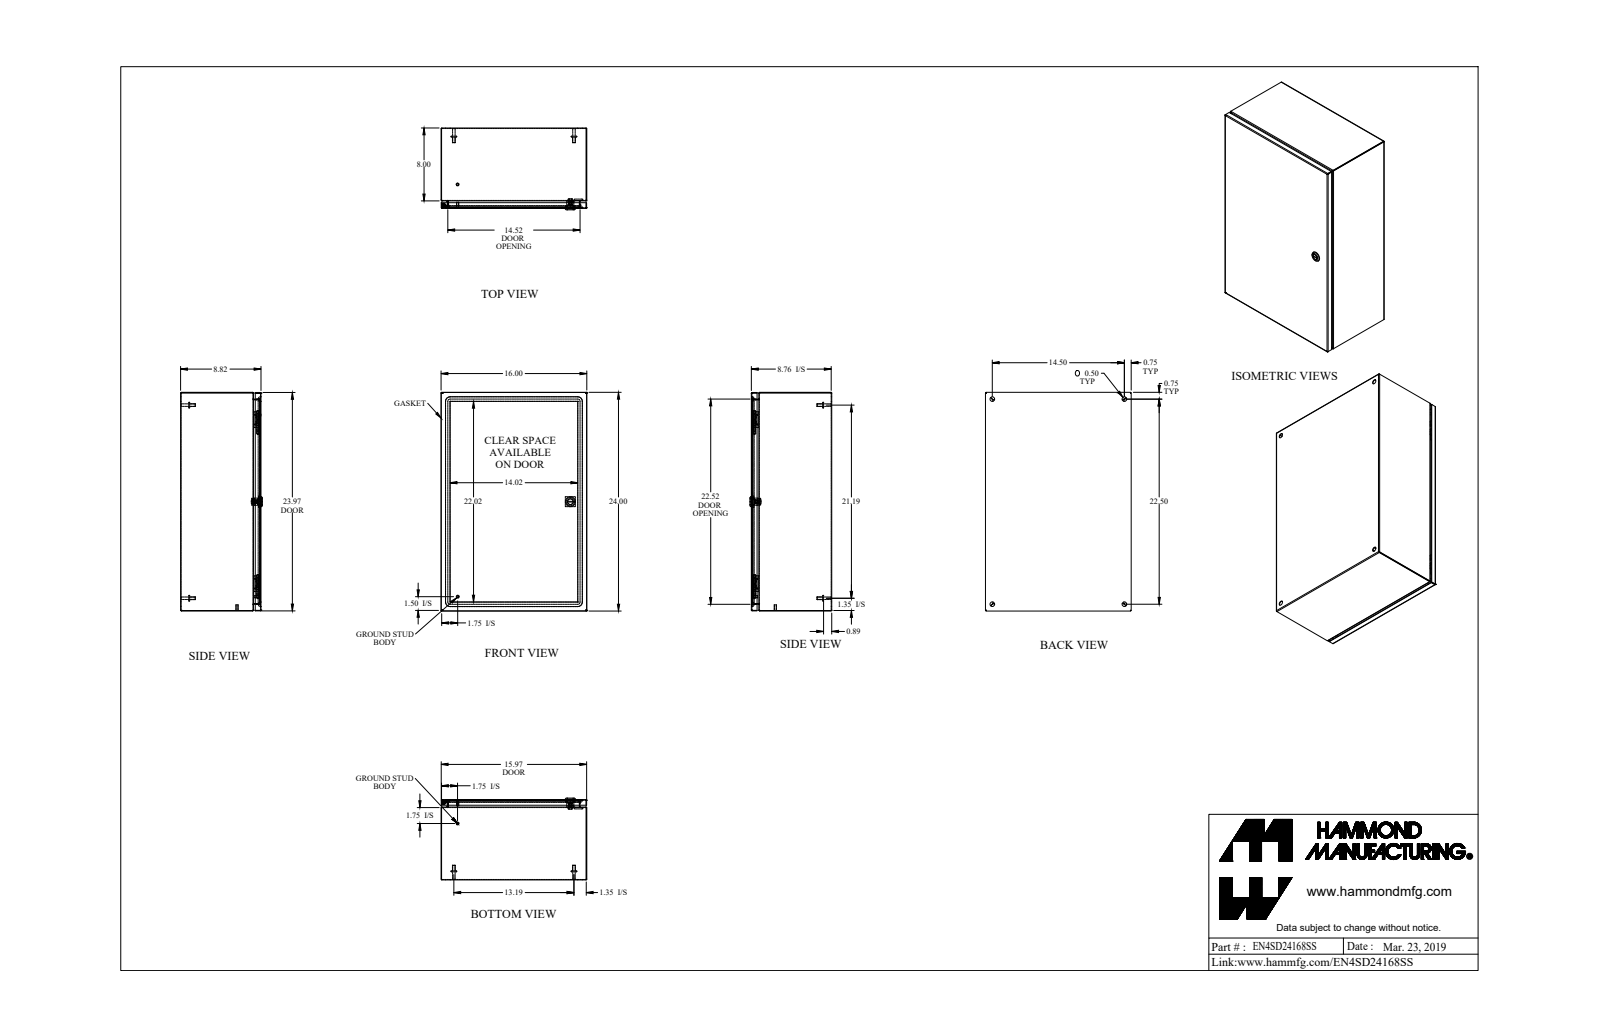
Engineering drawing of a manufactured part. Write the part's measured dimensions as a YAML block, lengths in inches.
part_name: "EN4SD24168SS_Default"
step_written_by: "SolidWorks 2019 (CONFIG_CONTROL_DESIGN)"
units: inches
bodies: {solids: 22, faces: 657, planar: 303, cylindrical: 212, other: 142}
overall_size: [24, 16, 8.982]
volume: 97.01
surface_area: 3308
round_holes:
  - {diameter: 0.5, count: 5}
  - {diameter: 0.172, count: 1}
  - {diameter: 0.197, count: 1}
  - {diameter: 0.24, count: 1}
  - {diameter: 0.242, count: 1}
  - {diameter: 0.387, count: 1}
  - {diameter: 0.63, count: 1}
  - {diameter: 0.768, count: 1}
round_bosses_or_shafts:
  - {diameter: 0.313, count: 6}
  - {diameter: 0.625, count: 4}
  - {diameter: 0.275, count: 4}
  - {diameter: 0.25, count: 2}
  - {diameter: 1.1, count: 1}
  - {diameter: 0.785, count: 1}
  - {diameter: 0.625, count: 1}
  - {diameter: 0.525, count: 1}
partial_cylinders:
  - {radius: 0.029, count: 21}
  - {radius: 0.086, count: 21}
  - {radius: 0.188, count: 12}
  - {radius: 0.006, count: 4}
  - {radius: 0.062, count: 4}
  - {radius: 0.25, count: 4}
  - {radius: 0.499, count: 4}
  - {radius: 0.125, count: 2}
face_to_face_distances: [0.057, 8.765, 8.708, 8.822, 15.943, 23.943, 15.886, 16, 23.886, 24]
hole_center_spacings: [11.3, 14.5, 17.528, 22.5, 26.767]
